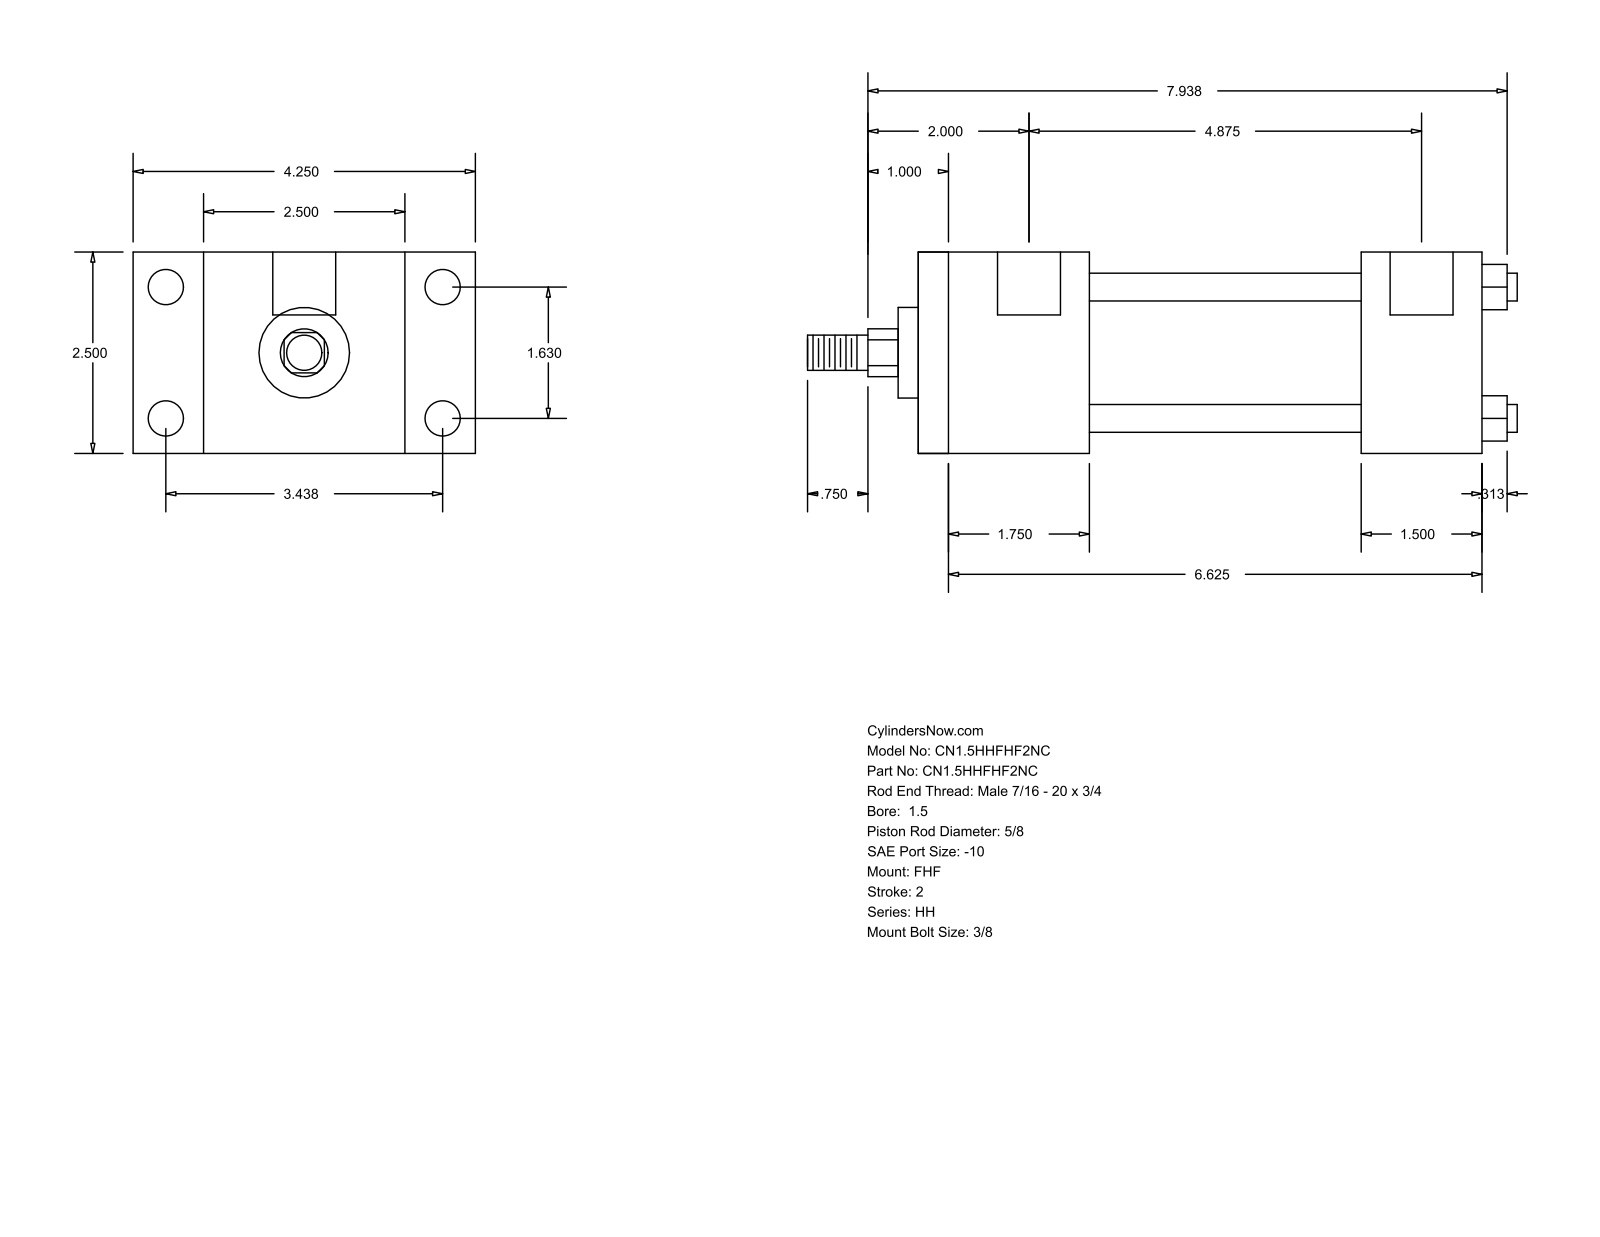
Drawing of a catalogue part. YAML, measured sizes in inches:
part_name: "HH_FHF__0150_0.625"
step_written_by: "GSSL Pune (CONFIG_CONTROL_DESIGN)"
units: inches
bodies: {solids: 0, faces: 88, planar: 60, cylindrical: 28, other: 0}
overall_size: [8.813, 4.25, 2.5]
round_holes:
  - {diameter: 0.219, count: 4}
  - {diameter: 0.438, count: 4}
  - {diameter: 0.781, count: 2}
round_bosses_or_shafts:
  - {diameter: 0.345, count: 4}
  - {diameter: 1.75, count: 1}
  - {diameter: 1.125, count: 1}
  - {diameter: 0.625, count: 1}
  - {diameter: 0.437, count: 1}
partial_cylinders:
  - {radius: 0.297, count: 1}
face_to_face_distances: [2.5, 0.875, 3.375, 2.125, 4.25, 7, 4.875, 3.375, 5.5, 1.5]
hole_center_spacings: [0.063, 1.63, 3.438, 3.805, 4.937, 5, 4.875]
